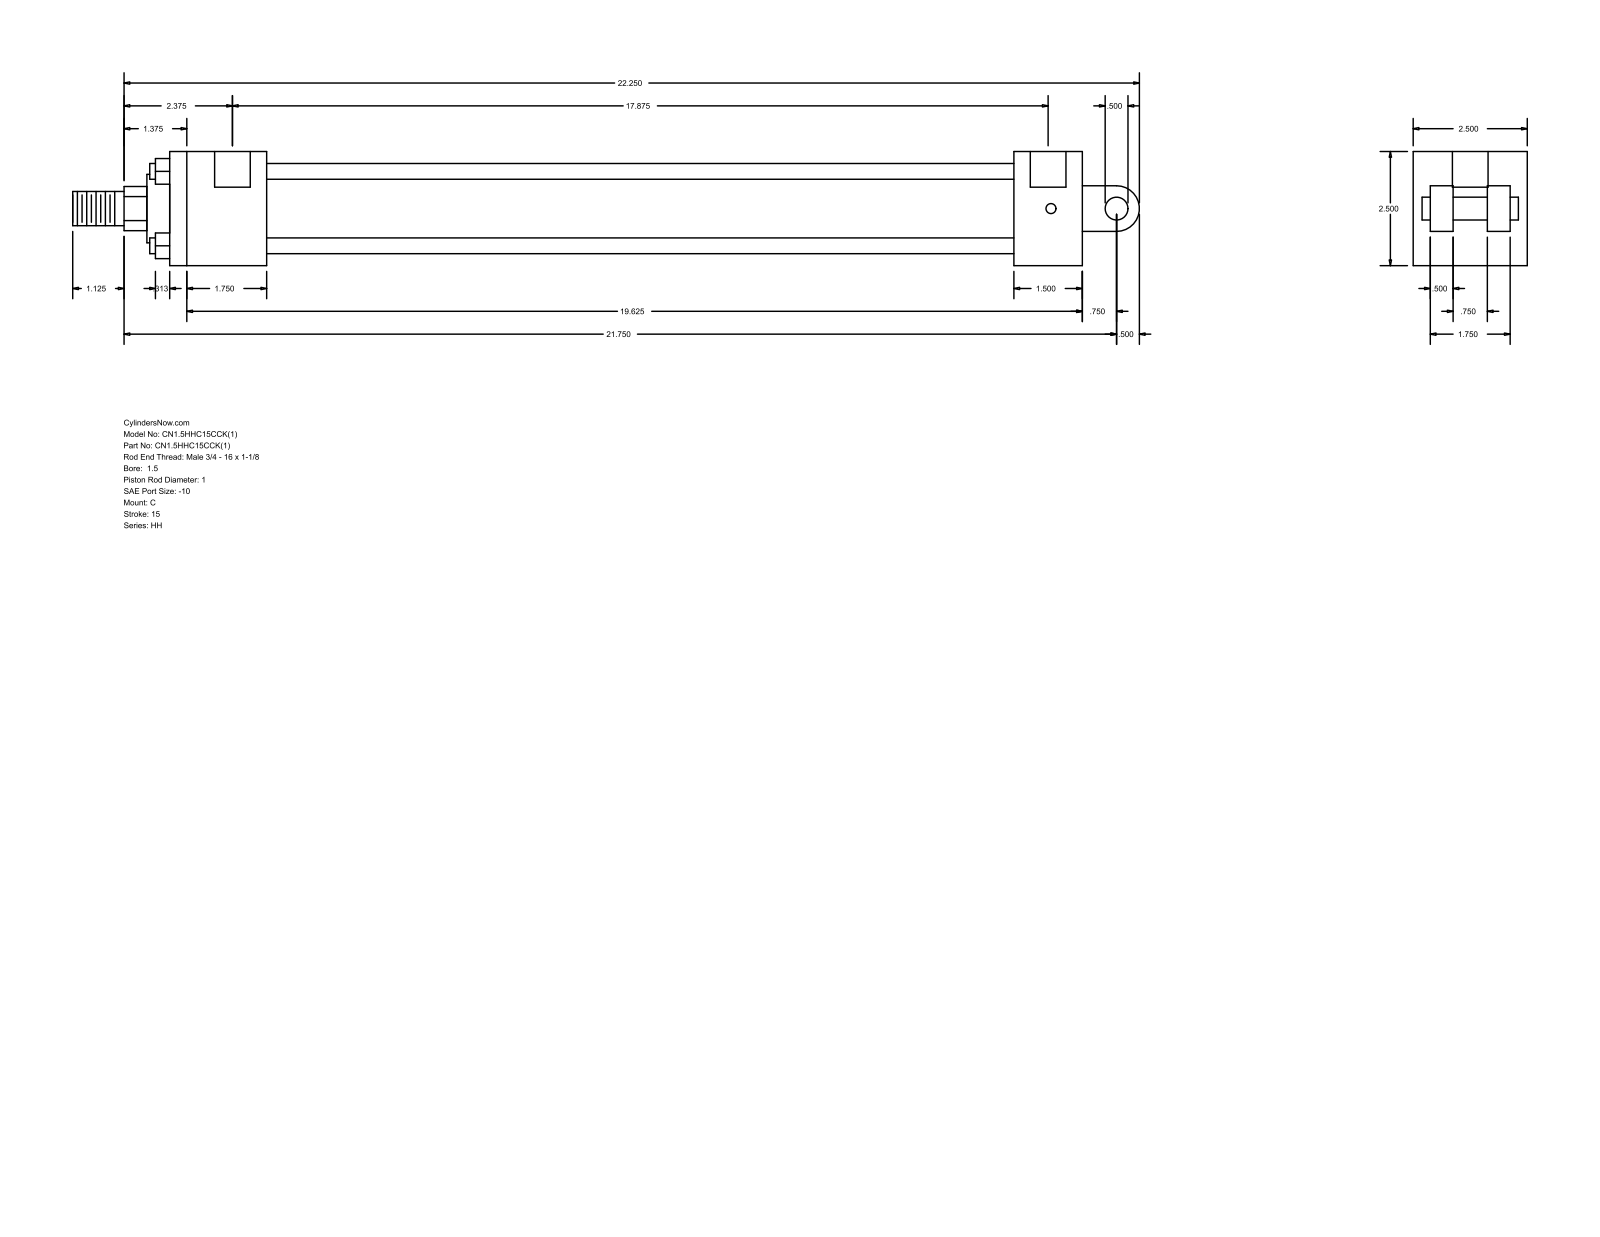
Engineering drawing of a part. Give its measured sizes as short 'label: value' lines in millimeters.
name: HH_C__0150_1
written by: GSSL Pune (CONFIG_CONTROL_DESIGN)
unit: mm
bodies: 0 solids, 99 faces (70 planar, 29 cylindrical, 0 other)
size: 593.73 × 63.5 × 63.5
holes: 4× ⌀5.56, 2× ⌀19.84
bosses: 4× ⌀8.76, 1× ⌀44.45, 1× ⌀38.1, 1× ⌀25.4, 1× ⌀19.05, 1× ⌀12.7
rounds: 1× R12.29, 1× R12.7
face distances: 63.5, 53.98, 38.1, 415.92, 454.02, 469.9, 508, 12.7, 9.52, 22.22
hole spacings: 1.59, 455.61, 457.2, 454.02
